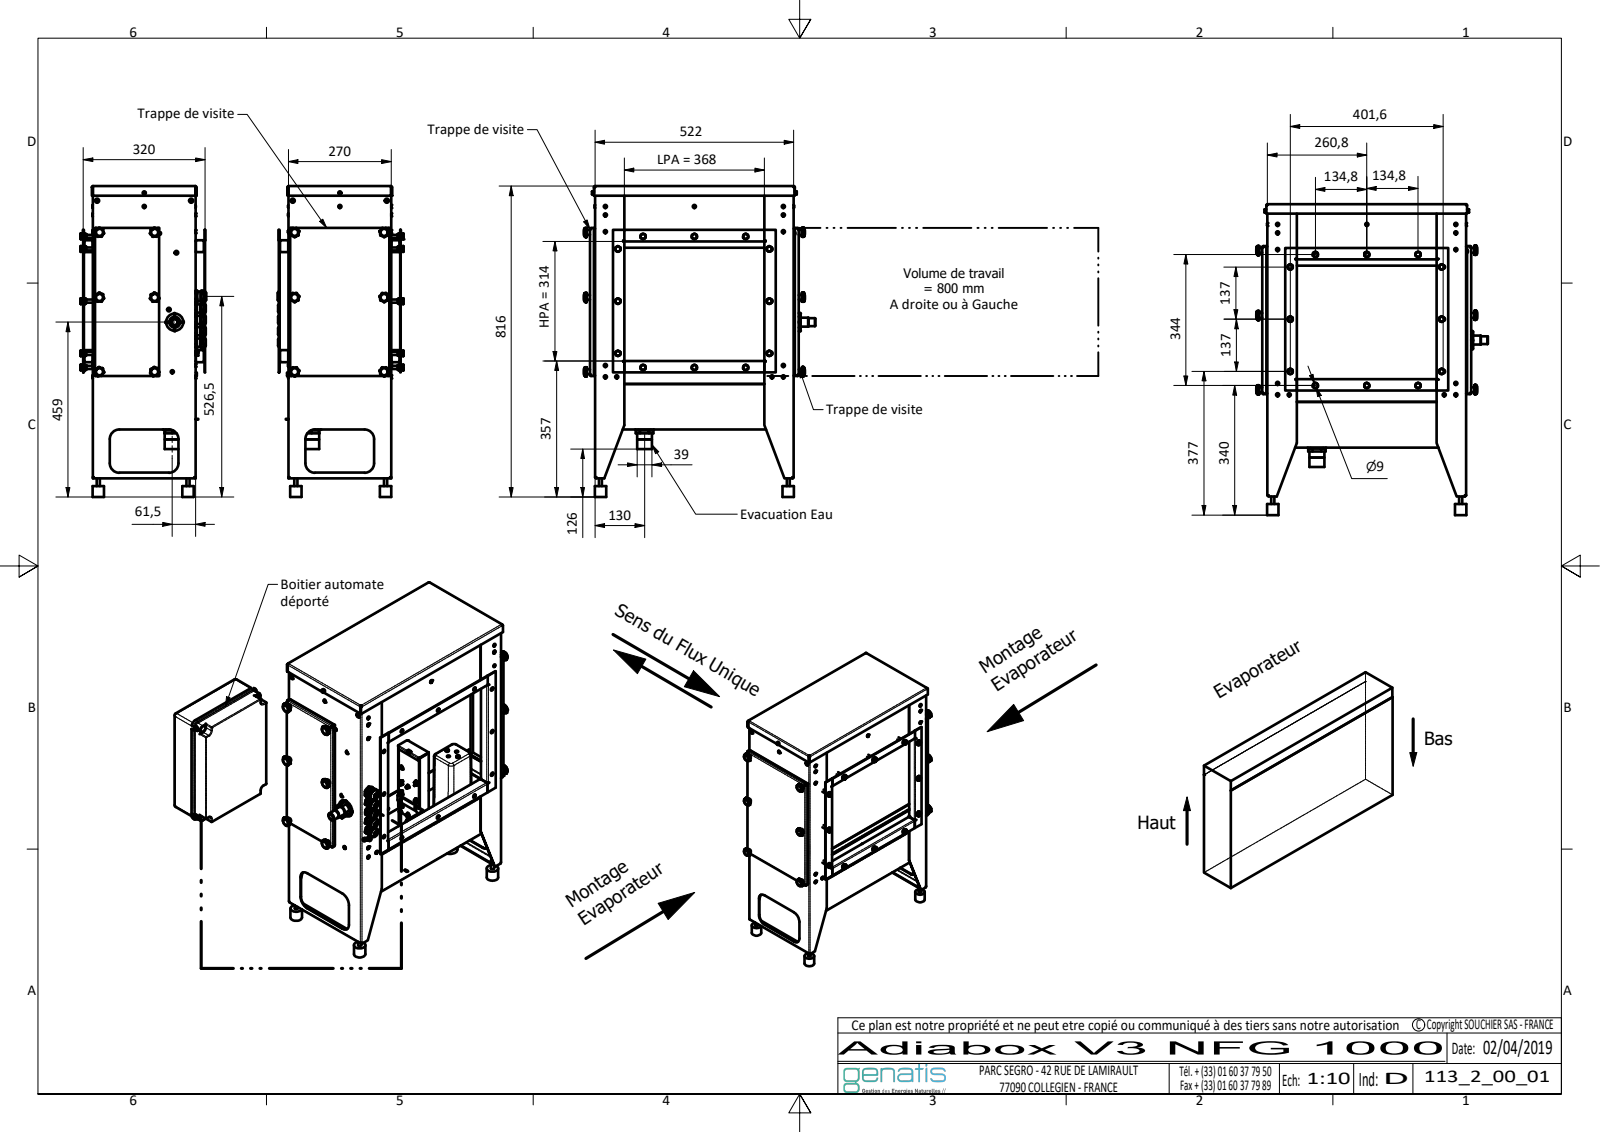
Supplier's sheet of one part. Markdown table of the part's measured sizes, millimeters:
| quantity | value |
| --- | --- |
| part name | 113_2_00_01_-_Adiabox_V3; 113_2_00_06_-_Glissiere basse assemblee; 113_3_00_11_-_Cote gauche glissiere; 113_3_00_15_-_Tole de fond pliee (+8 more) |
| STEP written by | Autodesk Inventor 2022 (AUTOMOTIVE_DESIGN) |
| units | millimeters |
| bodies | 274 solids, 8076 faces (4169 planar, 2295 cylindrical, 1612 other) |
| overall size | 816 × 608.1 × 323.5 |
| volume | 23 730 000 mm³ |
| surface area | 6 023 000 mm² |
| round holes (diameter × count) | 6 × 41, 4.1 × 38, 4.2 × 37, 3 × 34, 9 × 15, 7 × 13, 14 × 9, 1 × 8, 1.6 × 8, 2.1 × 8, 2.2 × 8, 5.2 × 8 |
| round bosses / shafts (diameter × count) | 11 × 40, 5 × 36, 7.9 × 34, 4 × 34, 7 × 33, 8.5 × 18, 2 × 10, 20 × 8 |
| partial cylindrical surfaces (radius × count) | 3 × 171, 1.5 × 86, 8 × 84, 1 × 37, 0.1 × 36, 0.3 × 36, 0.5 × 26, 2 × 19 |
| main face-to-face distances | 1.5, 2, 13.5, 533.6, 3, 266.5, 265, 532.1, 0.5, 267 |
| hole center spacings | 233.8, 467.6, 40, 100, 234.8, 2.6, 6.8, 7.4 |
